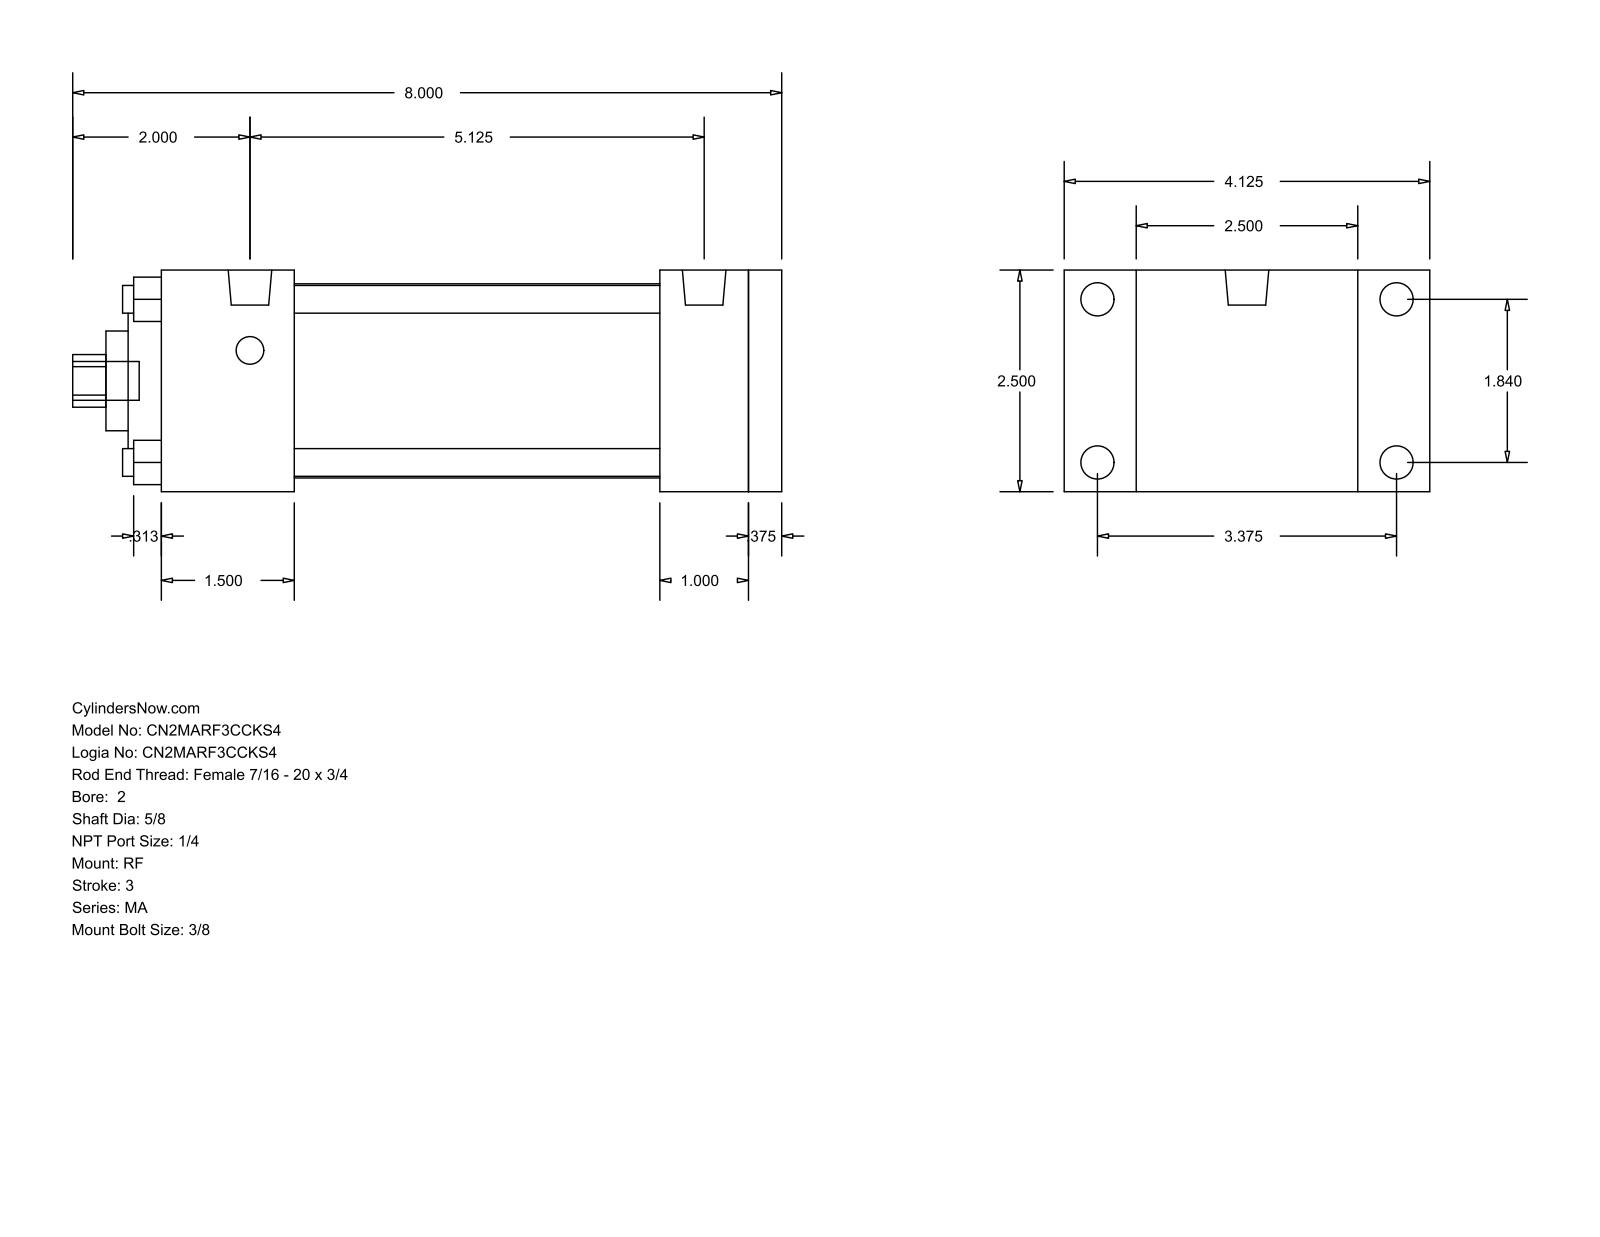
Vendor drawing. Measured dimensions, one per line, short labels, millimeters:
name: MA_RF__0200_0.625
written by: GSSL Pune (CONFIG_CONTROL_DESIGN)
unit: mm
bodies: 0 solids, 94 faces (65 planar, 29 cylindrical, 0 other)
size: 203.2 × 104.78 × 63.5
holes: 4× ⌀7.94, 1× ⌀15.88, 1× ⌀28.57, 1× ⌀50.8, 1× ⌀55.63
bosses: 4× ⌀9.53, 4× ⌀7.94, 2× ⌀12.49, 1× ⌀11.11
rounds: 1× R7.54
face distances: 63.5, 9.52, 177.8, 104.78, 25.4, 38.1, 168.28, 130.18, 139.7, 142.88
hole spacings: 33.05, 46.74, 66.1
